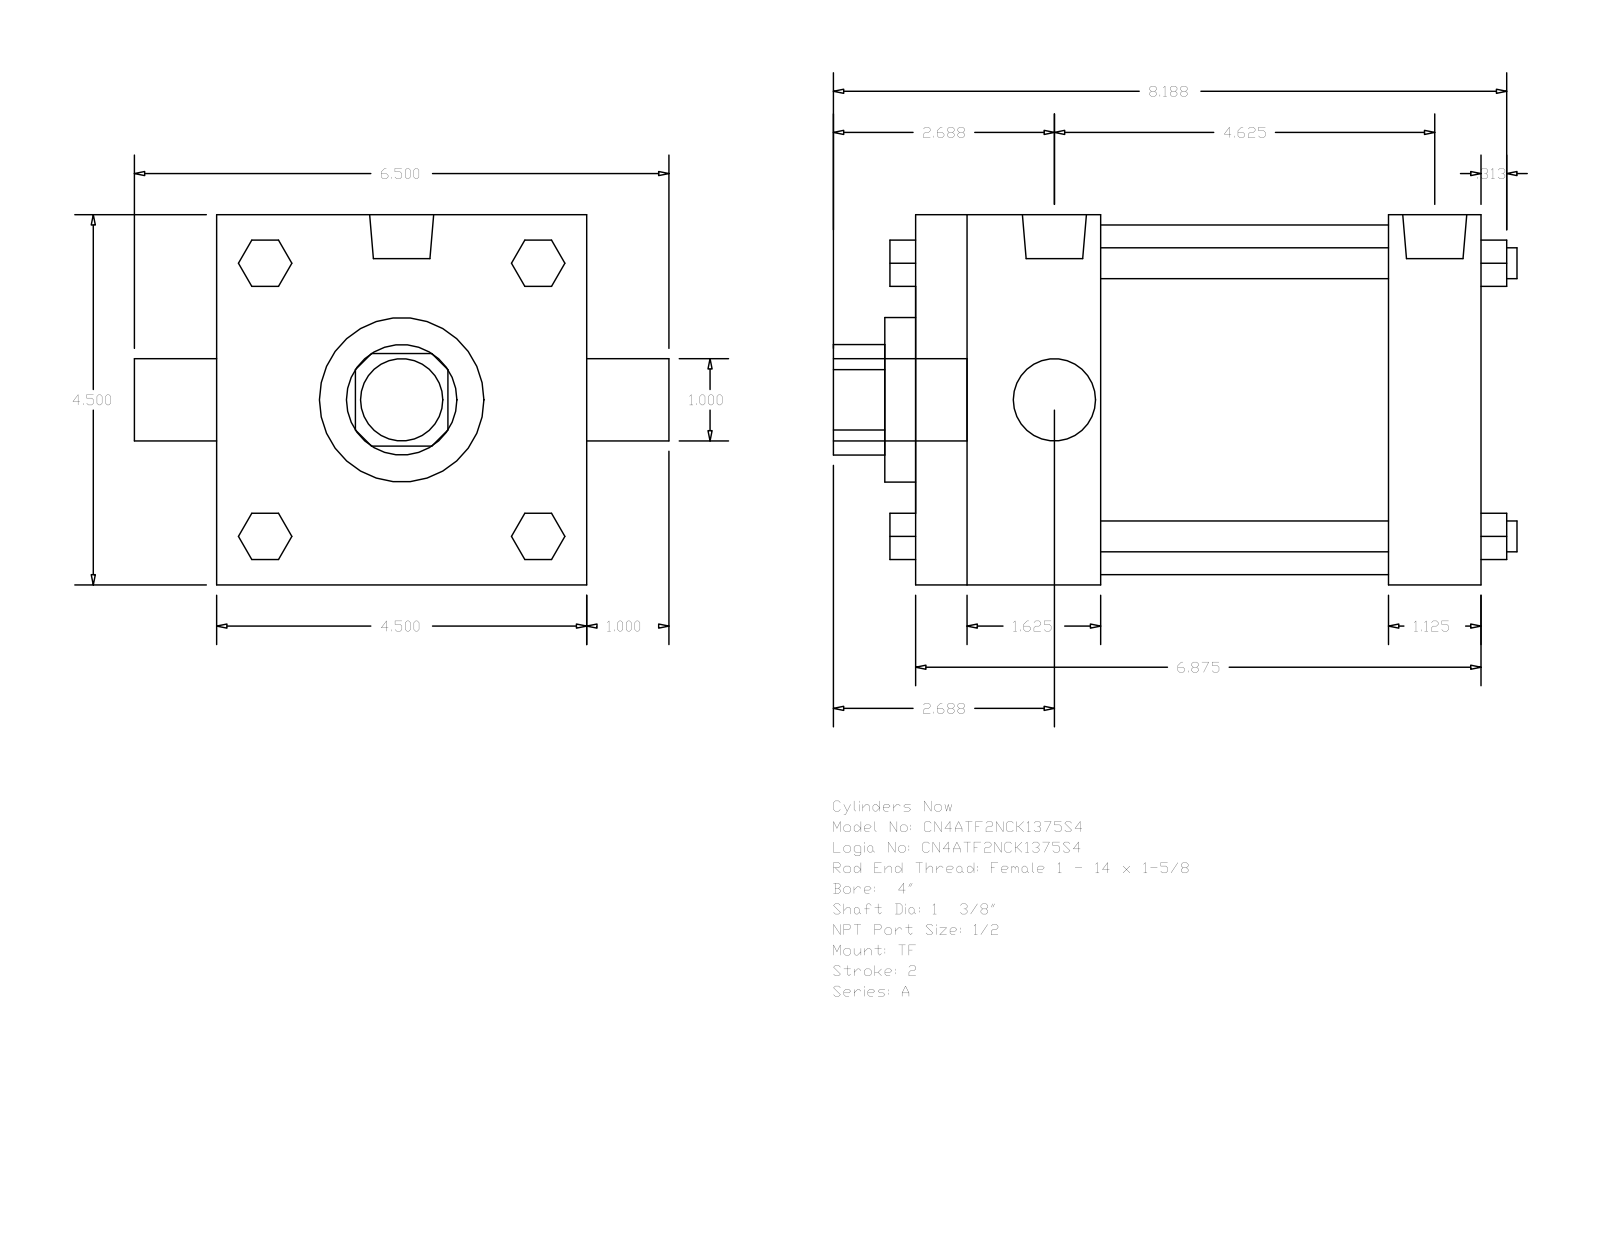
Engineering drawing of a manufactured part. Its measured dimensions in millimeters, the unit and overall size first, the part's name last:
Units: millimetres
Overall size (bounding box): 211.14 × 165.1 × 114.3
Round holes (diameter × count): ⌀25.4 ×1, ⌀34.92 ×1, ⌀50.8 ×1, ⌀107.95 ×1
Round bosses / shafts (diameter × count): ⌀9.53 ×4, ⌀8.73 ×3, ⌀19.77 ×2, ⌀25.4 ×1
Partial cylindrical surfaces — rounded edges, fillets, slot ends (radius × count): R17.06 ×1
Main face-to-face distances: 114.3, 174.63, 28.58, 146.05, 57.15, 88.9, 117.48, 14.29, 25.4, 9.52
Bodies: 0 solids, 120 faces (92 planar, 28 cylindrical, 0 other)
Part name (STEP PRODUCT): A_TF__0400_1.375
STEP written by: GSSL Pune (CONFIG_CONTROL_DESIGN)
